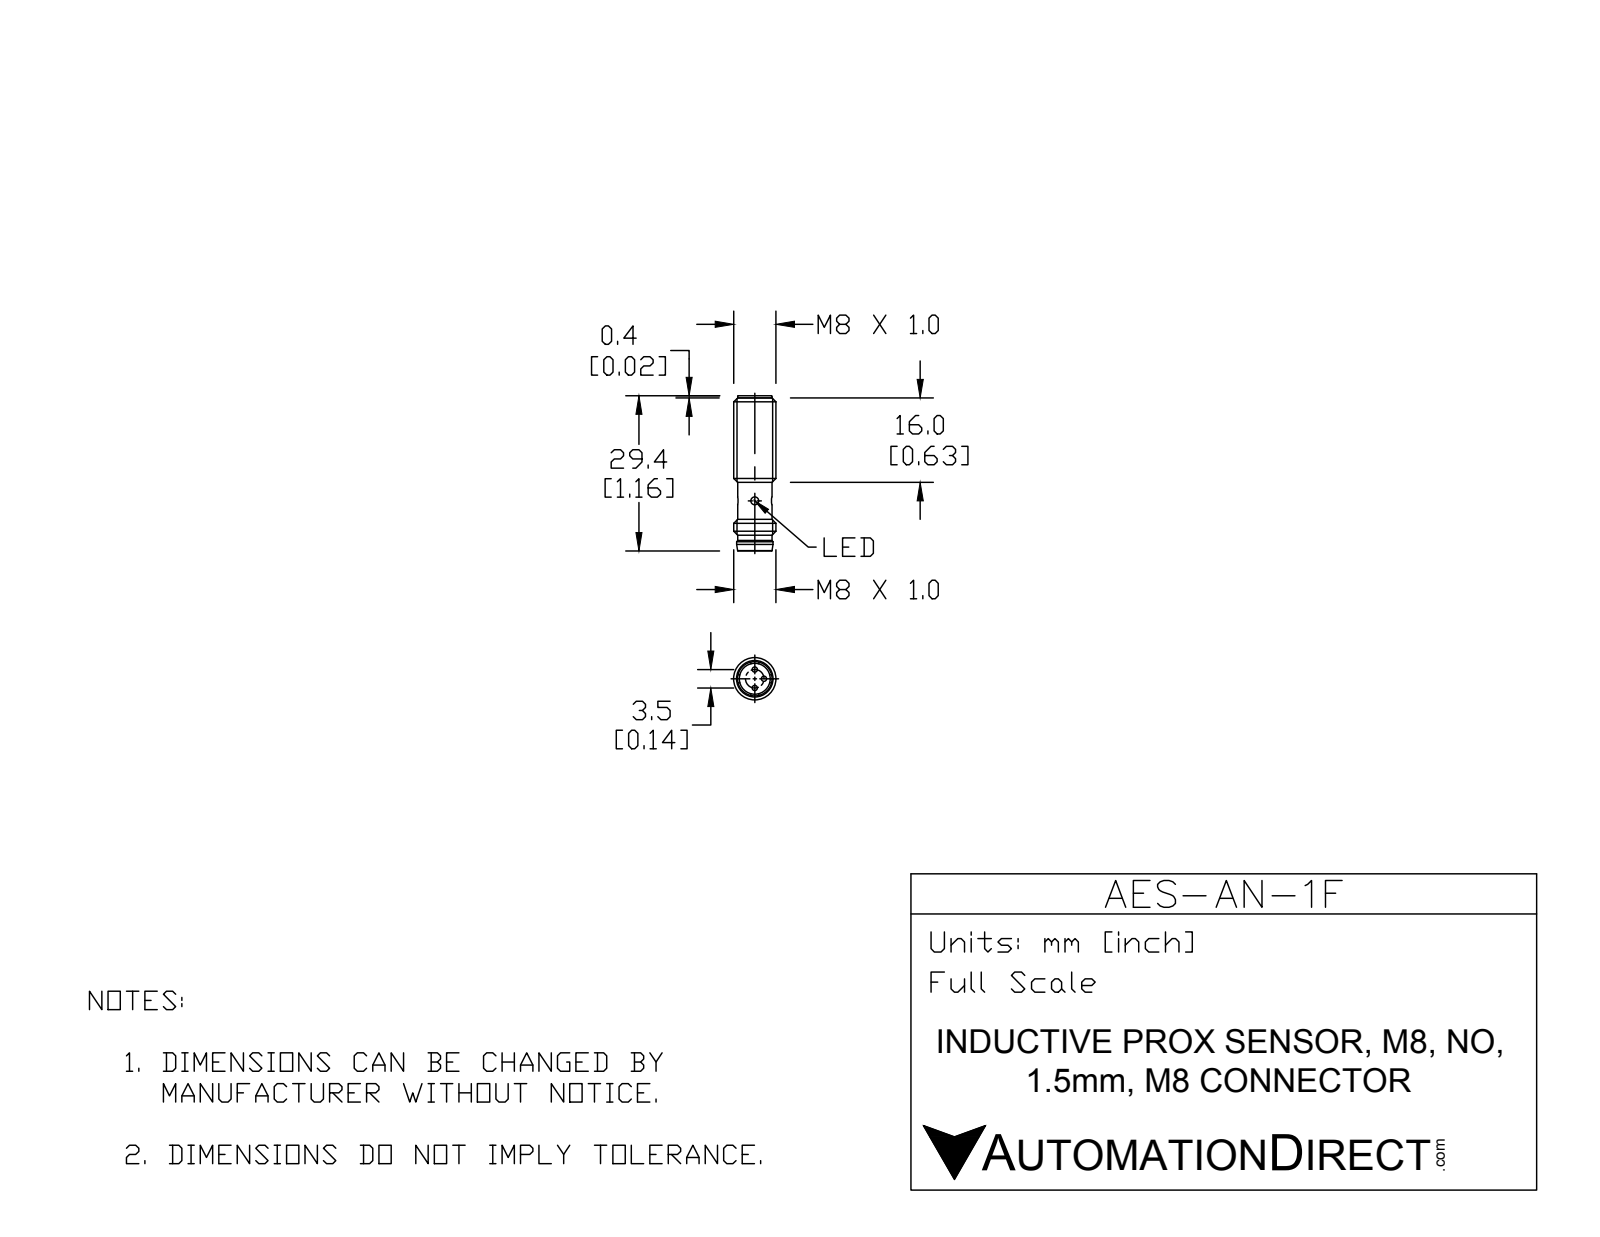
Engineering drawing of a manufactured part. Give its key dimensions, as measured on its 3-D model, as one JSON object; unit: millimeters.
{"part_name": "AES-AN-1F", "step_written_by": "SolidWorks 2015 (CONFIG_CONTROL_DESIGN)", "units": "millimeters", "bodies": {"solids": 1, "faces": 58, "planar": 10, "cylindrical": 28, "other": 20}, "overall_size": [29.4, 8, 8], "volume_mm3": 1157, "surface_area_mm2": 928, "round_holes": [[1.5, 2], [5.85, 1]], "round_bosses_or_shafts": [[1, 3], [8, 1], [6.9, 1], [6.5, 1]], "face_to_face_distances": [24.4, 3, 27.4, 5.5, 11, 8, 16.4, 27, 24, 16]}
